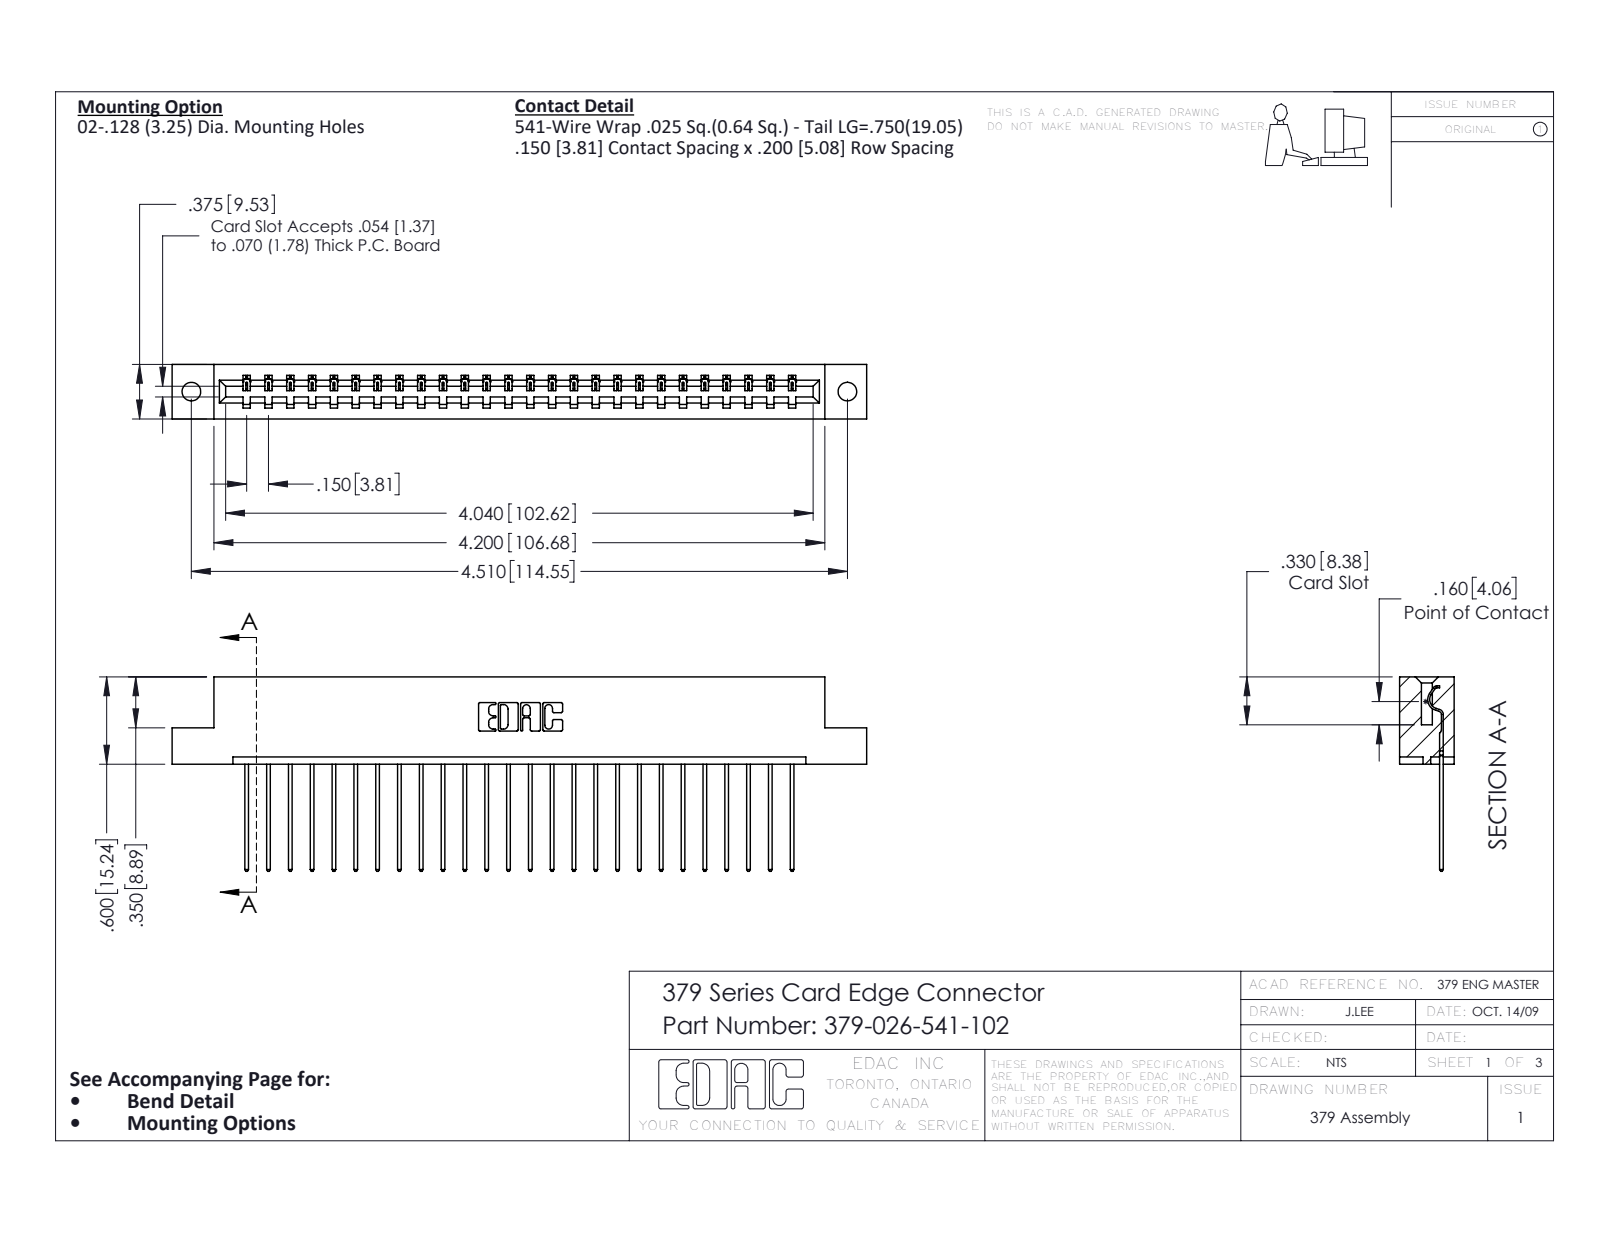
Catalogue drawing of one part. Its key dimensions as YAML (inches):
part_name: "379-026-541-102; 379 Part_Flush - .128 Dia; 345-292-001_345-293-141"
step_written_by: "SolidWorks 2016 (CONFIG_CONTROL_DESIGN)"
units: inches
bodies: {solids: 27, faces: 1622, planar: 1162, cylindrical: 460, other: 0}
overall_size: [4.775, 1.337, 0.375]
volume: 0.769
surface_area: 20.26
round_holes:
  - {diameter: 0.128, count: 2}
partial_cylinders:
  - {radius: 0.006, count: 52}
  - {radius: 0.01, count: 52}
  - {radius: 0.01, count: 22}
  - {radius: 0.007, count: 6}
  - {radius: 0.031, count: 6}
  - {radius: 0.026, count: 3}
  - {radius: 0.014, count: 1}
  - {radius: 0.022, count: 1}
face_to_face_distances: [0.3, 0.075, 0.375, 0.225, 0.6, 0.275, 0.1, 0.025, 0.2, 0.15]
hole_center_spacings: [4.51]
